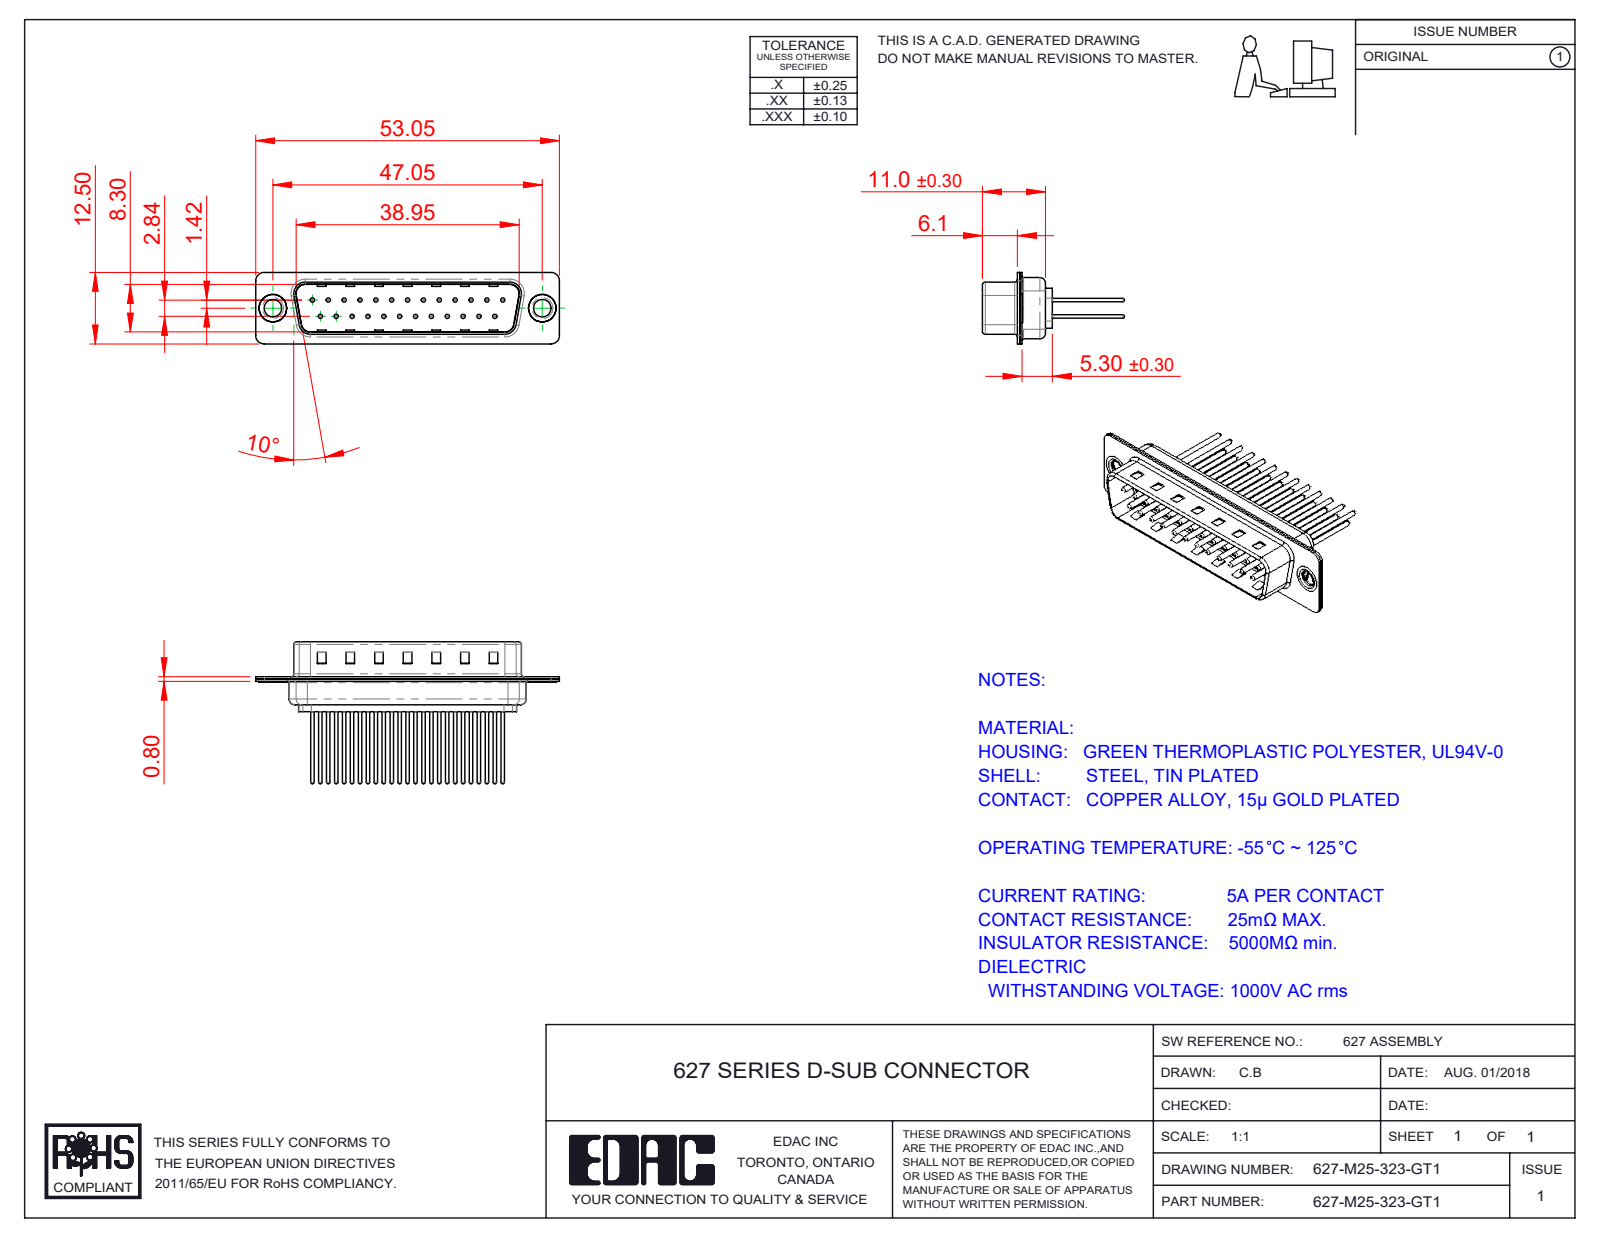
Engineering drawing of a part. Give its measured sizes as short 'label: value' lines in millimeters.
name: 627M Contact Row 1_23; 627M Shell Front_25 Contacts; 627M Housing_25 Contacts; 627M Thru Hole Rivet (+3 more)
written by: SolidWorks 2020 (CONFIG_CONTROL_DESIGN)
unit: mm
bodies: 30 solids, 1275 faces (346 planar, 471 cylindrical, 458 other)
size: 53.05 × 24.77 × 12.5
volume: 2 690 mm³; area: 7 022 mm²
holes: 25× ⌀0.75, 25× ⌀1.6, 25× ⌀2, 2× ⌀3.05, 2× ⌀4, 2× ⌀4.8
bosses: 25× ⌀1.5, 25× ⌀0.6, 2× ⌀5, 2× ⌀4.9, 2× ⌀3.55
rounds: 16× R1.5, 12× R2, 8× R0.5, 8× R1.6, 4× R0.25, 4× R0.6, 4× R0.65, 4× R0.9
face distances: 0.4, 0.8, 9.5, 9.1, 8.7, 9.9, 1.2, 6.1, 5.7, 0.75
hole spacings: 3.16, 2.77, 5.54, 8.31, 11.08, 13.85, 16.62, 5.03
